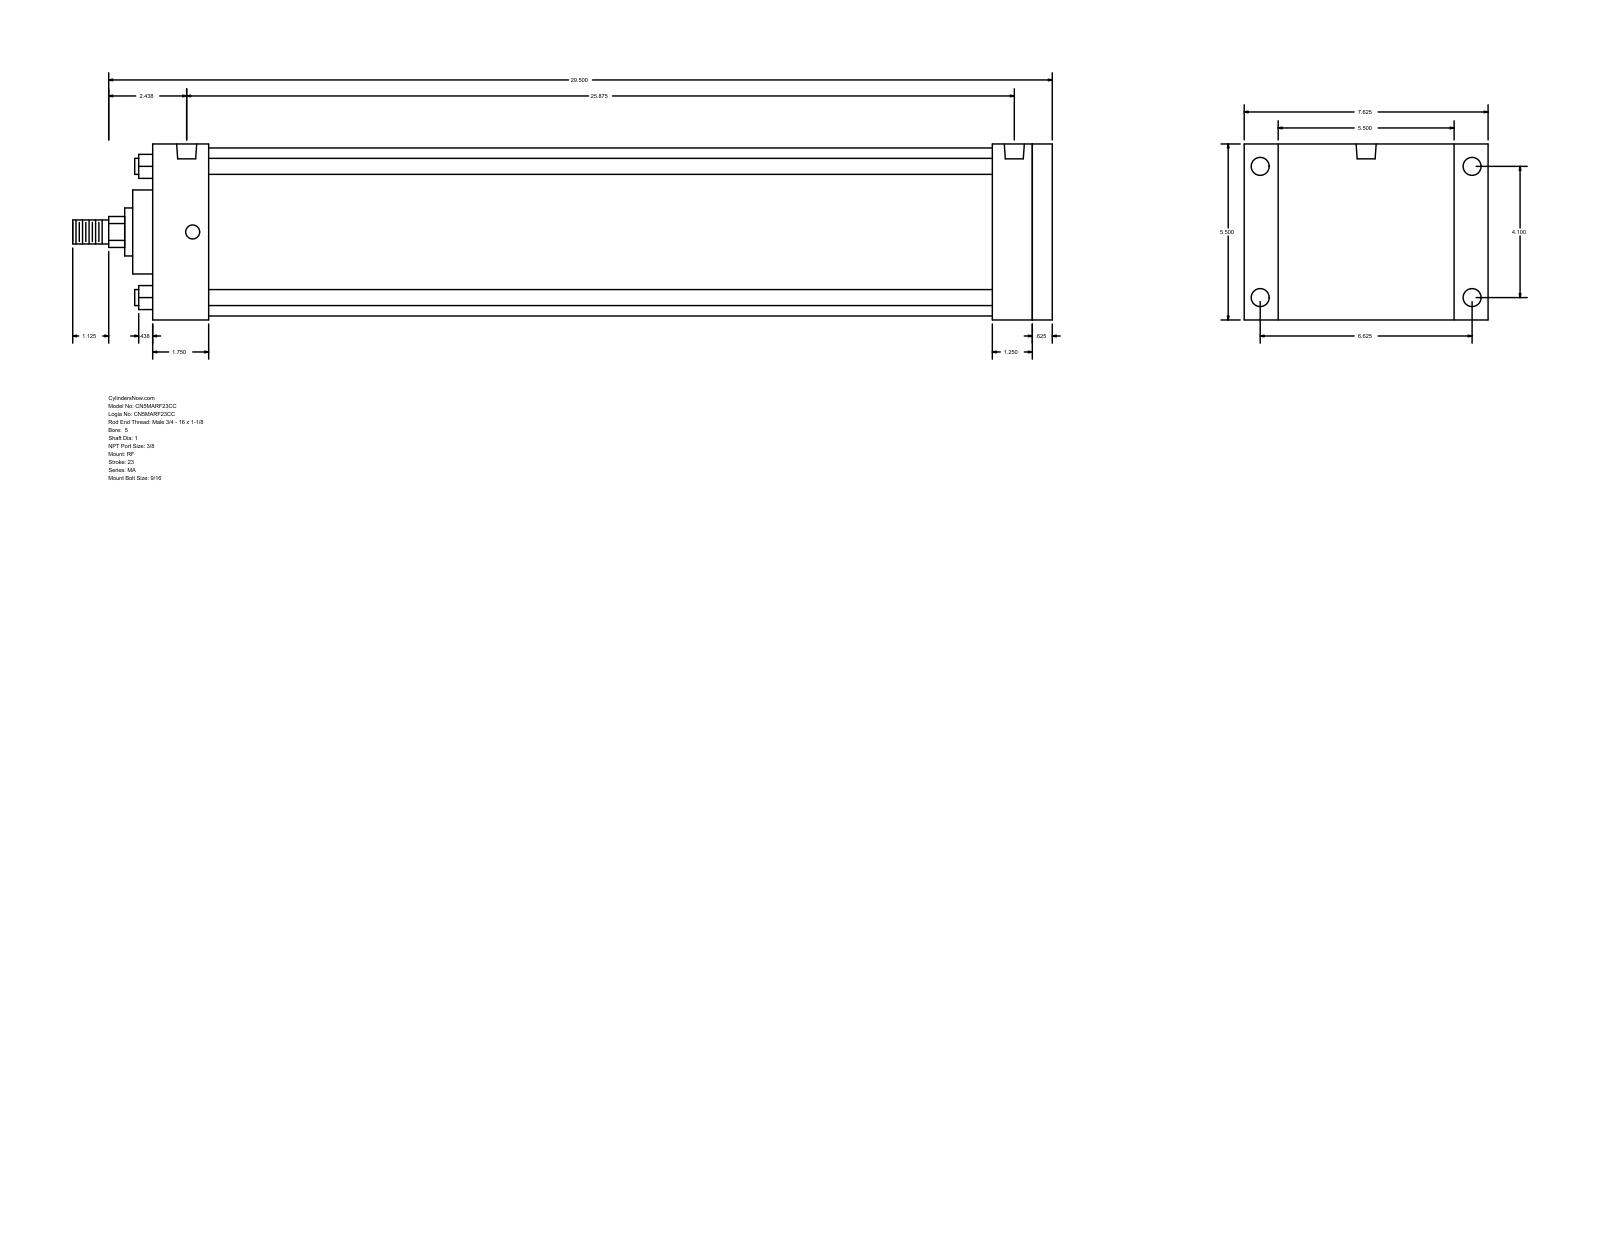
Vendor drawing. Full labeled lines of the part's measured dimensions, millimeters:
Part name (STEP PRODUCT): MA_RF__0500_1
STEP written by: GSSL Pune (CONFIG_CONTROL_DESIGN)
Units: millimetres
Bodies: 0 solids, 94 faces (65 planar, 29 cylindrical, 0 other)
Overall size (bounding box): 777.88 × 193.68 × 139.7
Round holes (diameter × count): ⌀11.11 ×4, ⌀14.29 ×4, ⌀15.93 ×2
Round bosses / shafts (diameter × count): ⌀12.7 ×4, ⌀133.35 ×1, ⌀66.67 ×1, ⌀38.1 ×1, ⌀25.4 ×1, ⌀19.05 ×1
Partial cylindrical surfaces — rounded edges, fillets, slot ends (radius × count): R12.29 ×1
Main face-to-face distances: 139.7, 714.38, 698.5, 15.88, 44.46, 654.04, 669.92, 666.75, 622.29, 31.75
Hole centre spacings: 4.76, 104.14, 168.28, 197.9, 647.71, 652.47, 657.23
